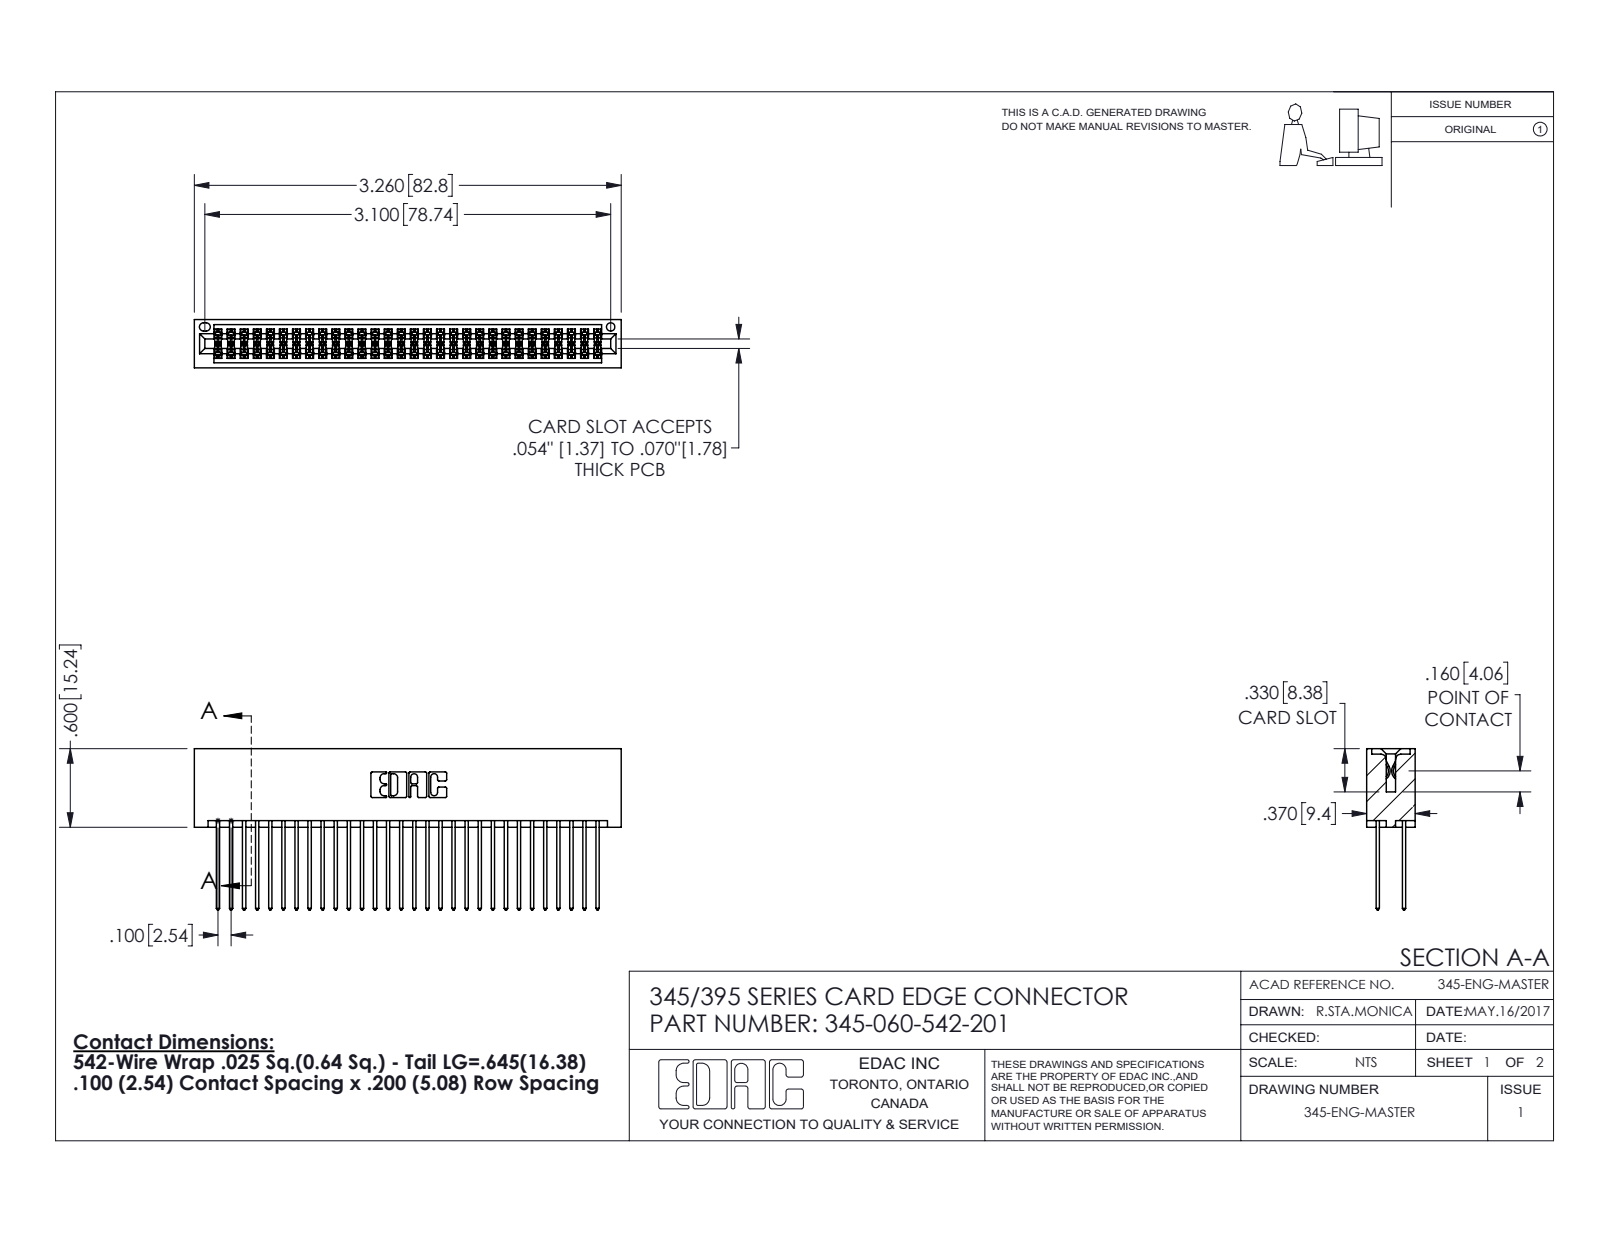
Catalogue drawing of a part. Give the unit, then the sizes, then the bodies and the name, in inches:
Units: inches
Overall size (bounding box): 3.26 × 1.232 × 0.37
Round holes (diameter × count): ⌀0.064 ×1
Partial cylindrical surfaces — rounded edges, fillets, slot ends (radius × count): R0.006 ×90, R0.01 ×60, R0.01 ×22, R0.007 ×6, R0.031 ×6, R0.026 ×3, R0.014 ×2, R0.019 ×2
Main face-to-face distances: 0.298, 0.072, 0.2, 0.098, 0.272, 0.025, 0.225, 0.37, 0.175, 0.149
Volume: 0.539 in³ · Surface area: 22.36 in²
Bodies: 61 solids, 3118 faces (2056 planar, 1062 cylindrical, 0 other)
Part name (STEP PRODUCT): 345 Part_No Mounting Lugs; 345-060-542-201; 345-292-001_345-293-142
STEP written by: SolidWorks 2016 (CONFIG_CONTROL_DESIGN)
